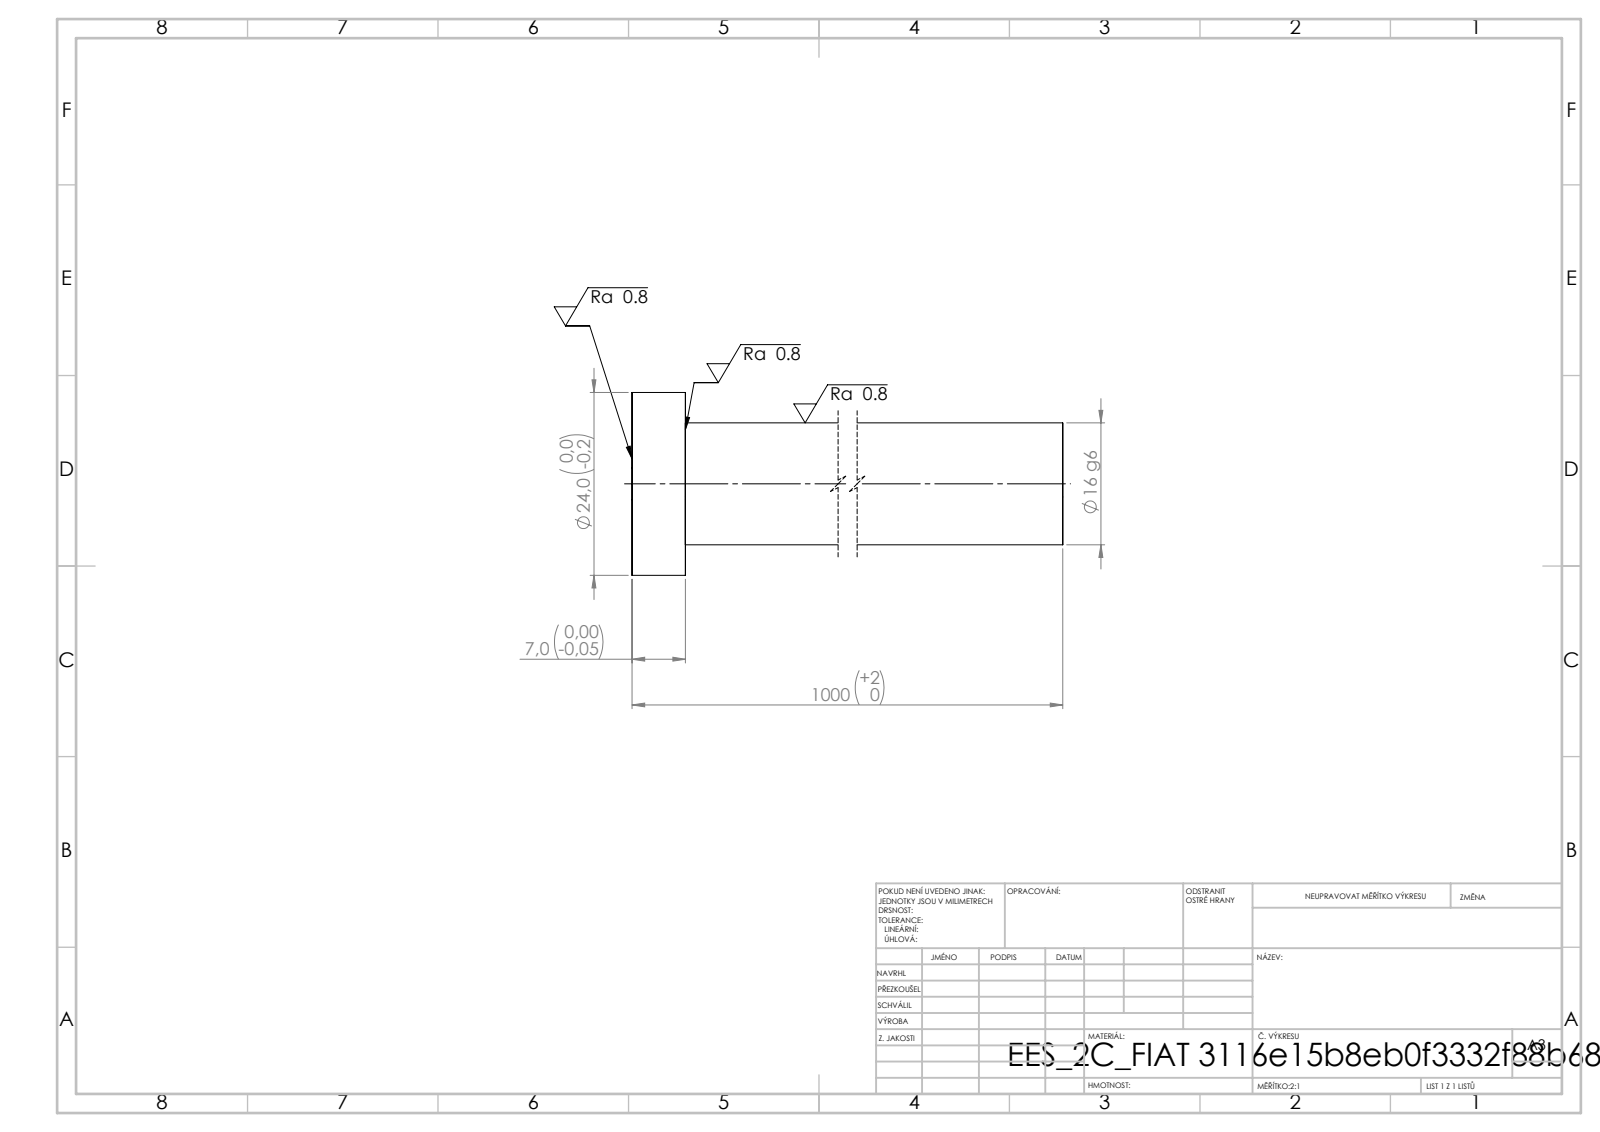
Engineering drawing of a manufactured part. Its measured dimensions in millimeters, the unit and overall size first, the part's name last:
Units: millimetres
Overall size (bounding box): 1000 × 24 × 24
Round bosses / shafts (diameter × count): ⌀24 ×1, ⌀16 ×1
Main face-to-face distances: 7, 1000, 993
Volume: 202 821 mm³ · Surface area: 51 346 mm²
Bodies: 1 solid, 7 faces (3 planar, 4 cylindrical, 0 other)
STEP written by: SolidWorks 2019 (CONFIG_CONTROL_DESIGN)
